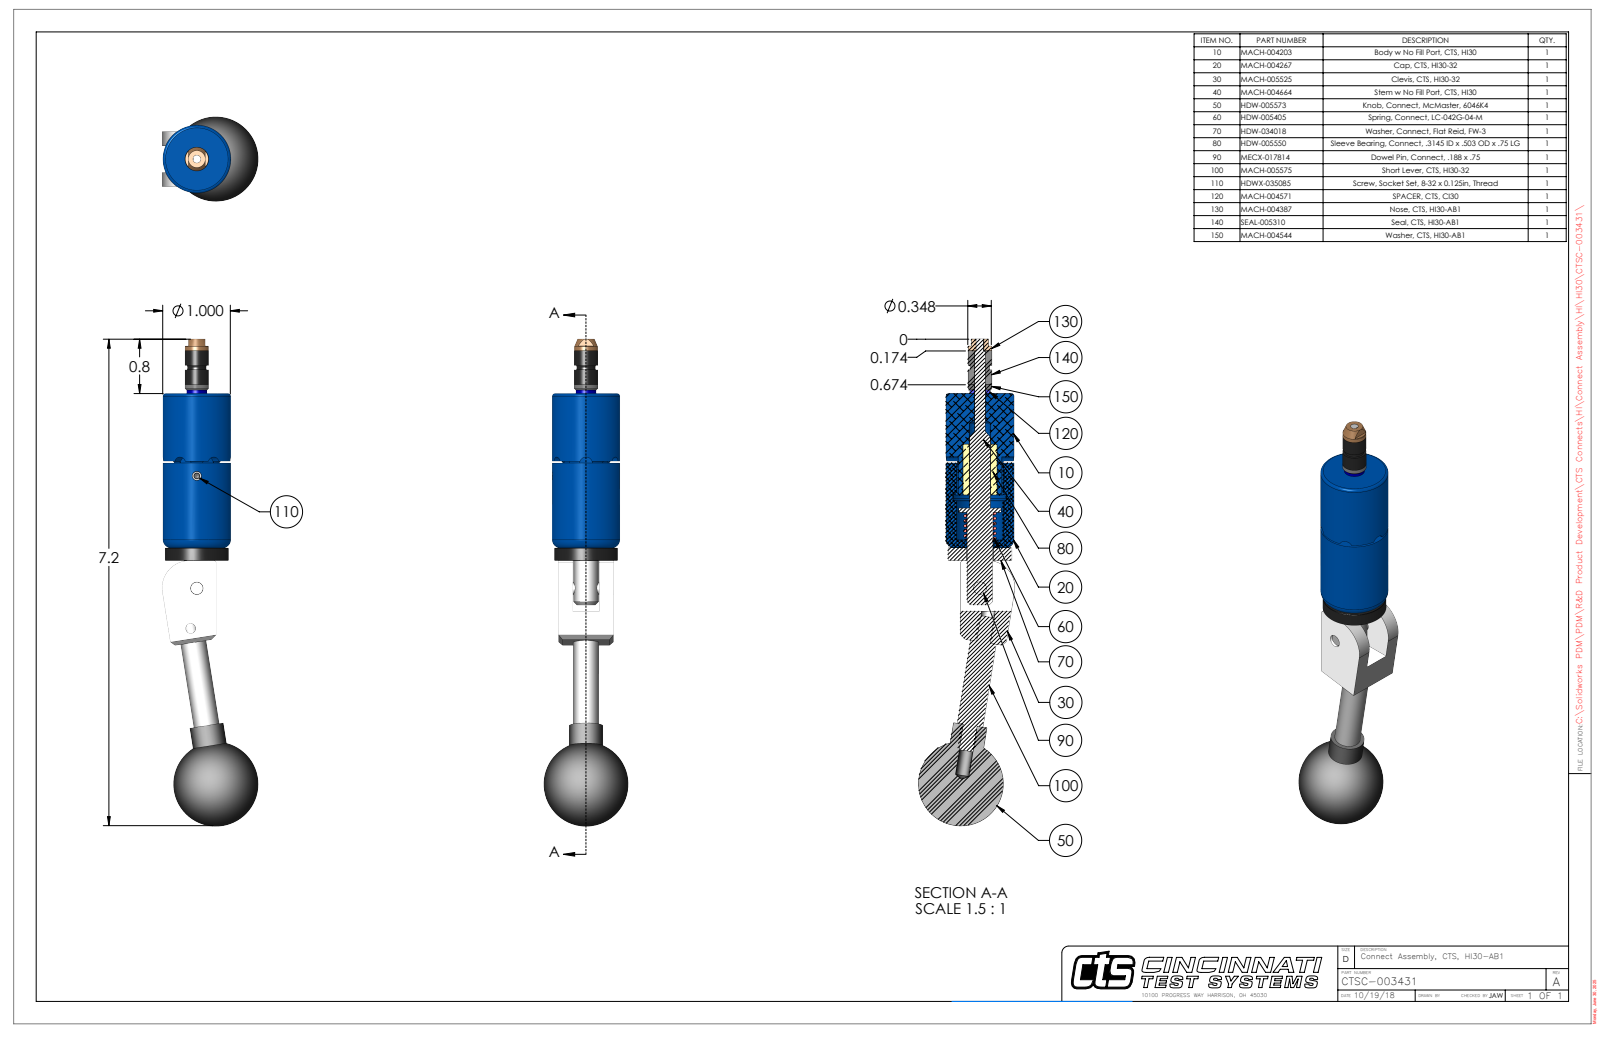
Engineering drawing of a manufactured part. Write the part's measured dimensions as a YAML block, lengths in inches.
part_name: "CTSC-003431"
step_written_by: "SolidWorks 2023 (AUTOMOTIVE_DESIGN)"
units: inches
bodies: {solids: 10, faces: 252, planar: 96, cylindrical: 99, other: 57}
overall_size: [7.193, 1.416, 1.25]
volume: 3.725
surface_area: 29.61
round_holes:
  - {diameter: 0.201, count: 2}
  - {diameter: 0.113, count: 1}
  - {diameter: 0.136, count: 1}
  - {diameter: 0.15, count: 1}
  - {diameter: 0.155, count: 1}
  - {diameter: 0.161, count: 1}
  - {diameter: 0.164, count: 1}
  - {diameter: 0.189, count: 1}
  - {diameter: 0.385, count: 1}
  - {diameter: 0.392, count: 1}
round_bosses_or_shafts:
  - {diameter: 1, count: 1}
  - {diameter: 0.936, count: 1}
  - {diameter: 0.5, count: 1}
  - {diameter: 0.38, count: 1}
  - {diameter: 0.375, count: 1}
  - {diameter: 0.35, count: 1}
  - {diameter: 0.347, count: 1}
  - {diameter: 0.3, count: 1}
partial_cylinders:
  - {radius: 0.093, count: 6}
  - {radius: 0.015, count: 1}
  - {radius: 0.344, count: 1}
  - {radius: 0.4, count: 1}
  - {radius: 0.481, count: 1}
face_to_face_distances: [0.21, 0.602, 0.812, 0.187, 2.28, 2.467, 0.391, 1.026, 1.253, 1.441]
hole_center_spacings: [0.599, 1.658, 2.252]
